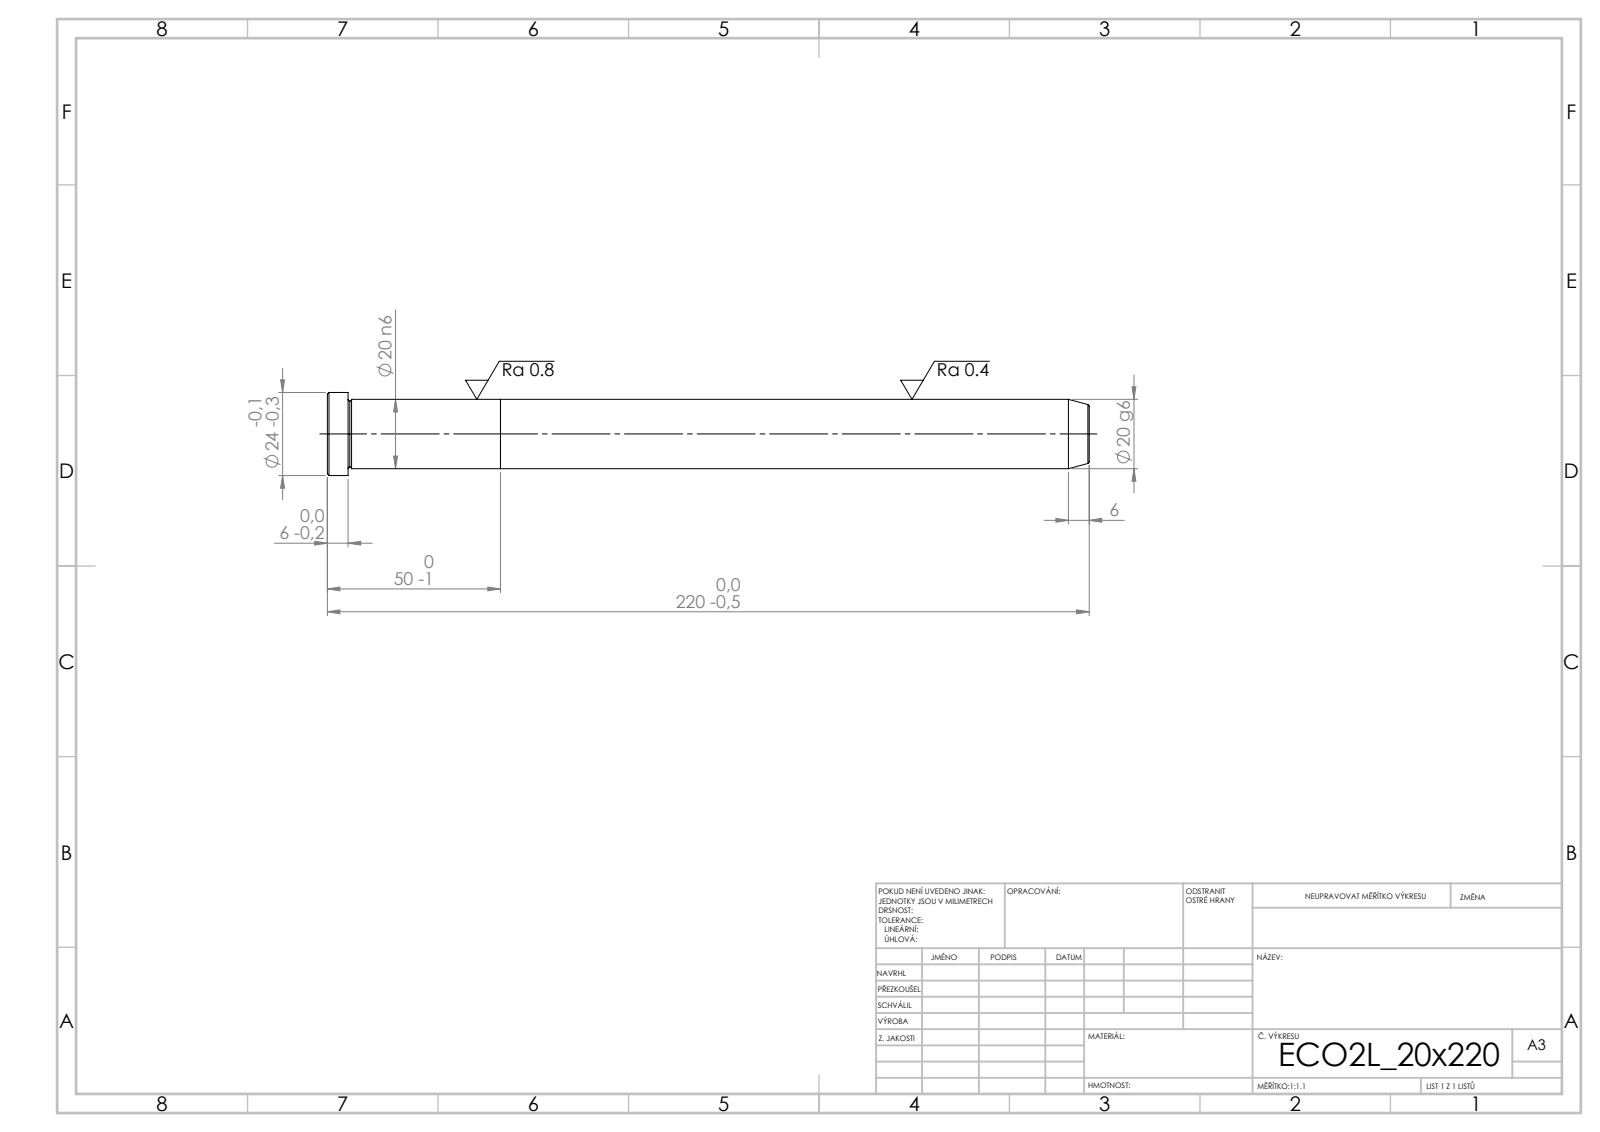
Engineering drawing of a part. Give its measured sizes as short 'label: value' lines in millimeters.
written by: SolidWorks 2019 (CONFIG_CONTROL_DESIGN)
unit: mm
bodies: 2 solids, 21 faces (5 planar, 6 cylindrical, 10 other)
size: 220 × 24 × 24
volume: 69 623 mm³; area: 15 325 mm²
bosses: 1× ⌀24, 1× ⌀20
face distances: 50, 170, 220, 214, 44, 6
